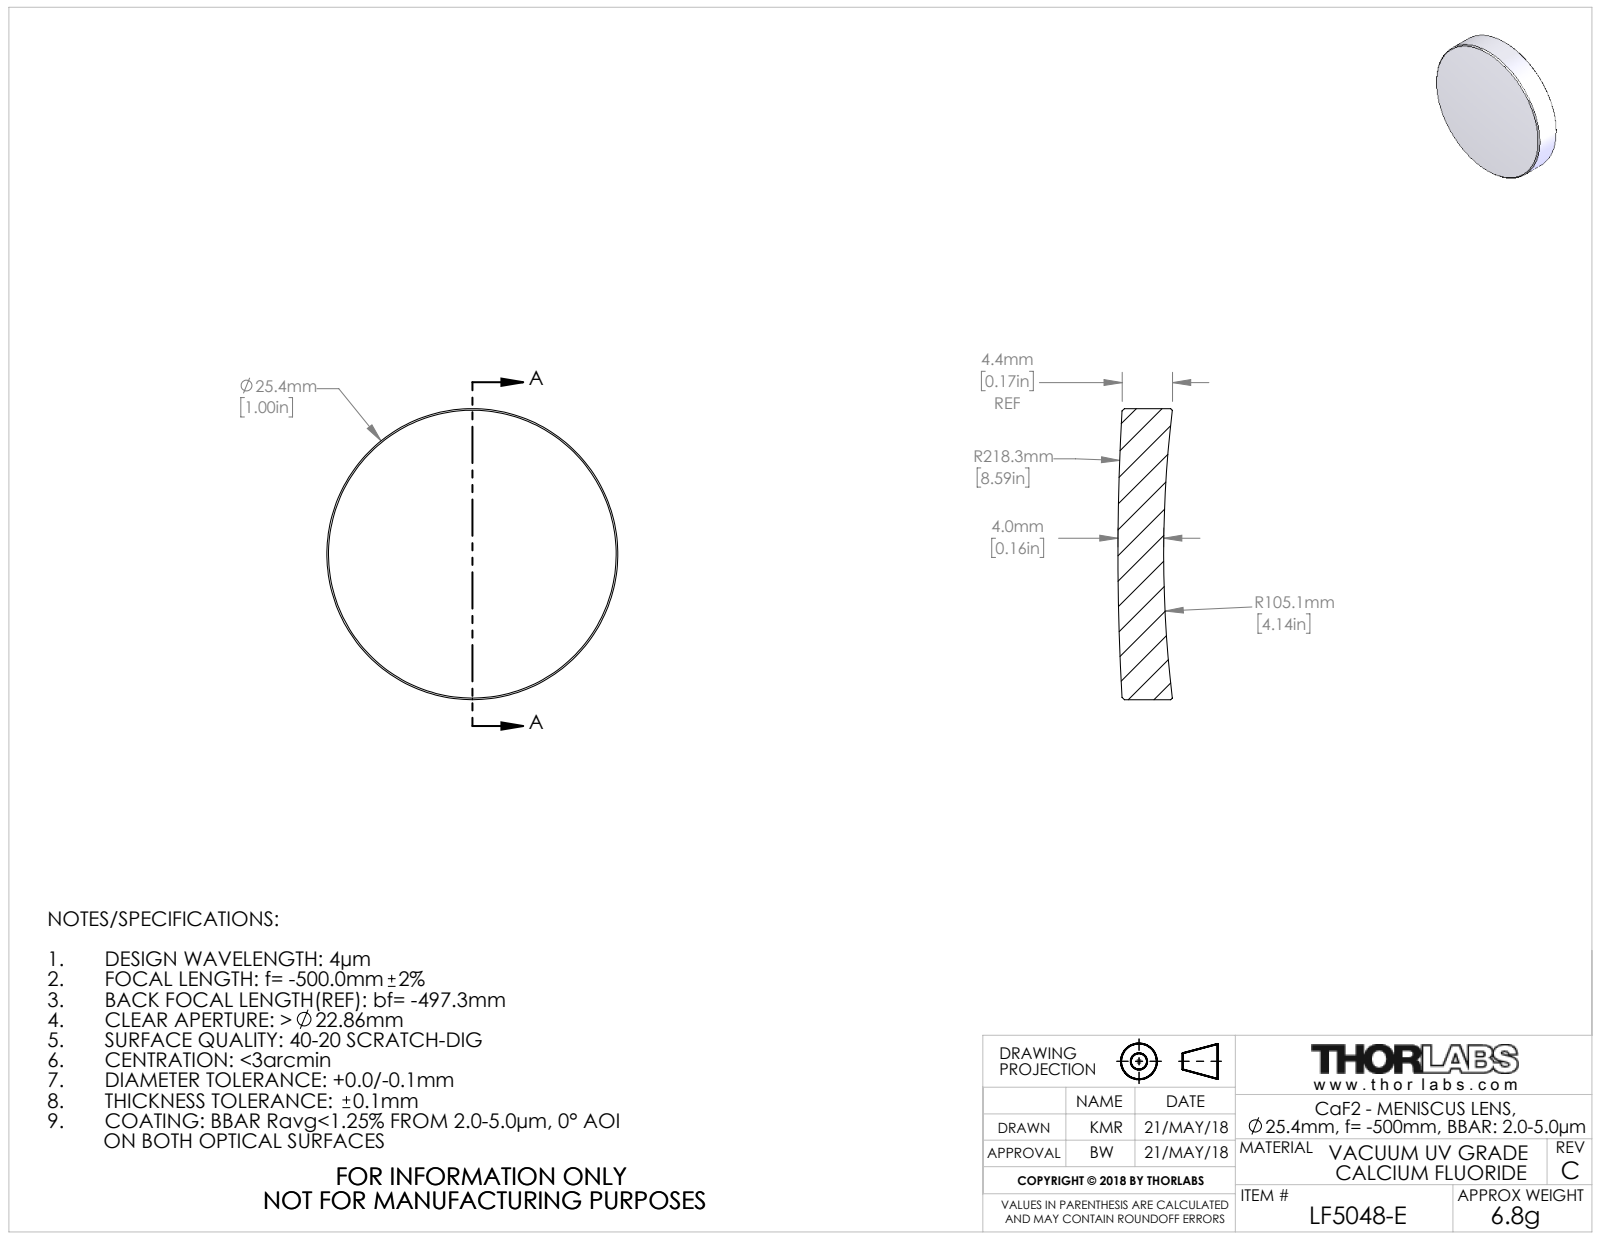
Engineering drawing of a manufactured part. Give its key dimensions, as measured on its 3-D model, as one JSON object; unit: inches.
{"part_name": "20178-E0W", "step_written_by": "SolidWorks 2016 (CONFIG_CONTROL_DESIGN)", "units": "inches", "bodies": {"solids": 1, "faces": 10, "planar": 0, "cylindrical": 2, "other": 8}, "overall_size": [1, 1, 0.187], "volume_in3": 0.13, "surface_area_in2": 2.092, "round_bosses_or_shafts": [[1, 1]]}
